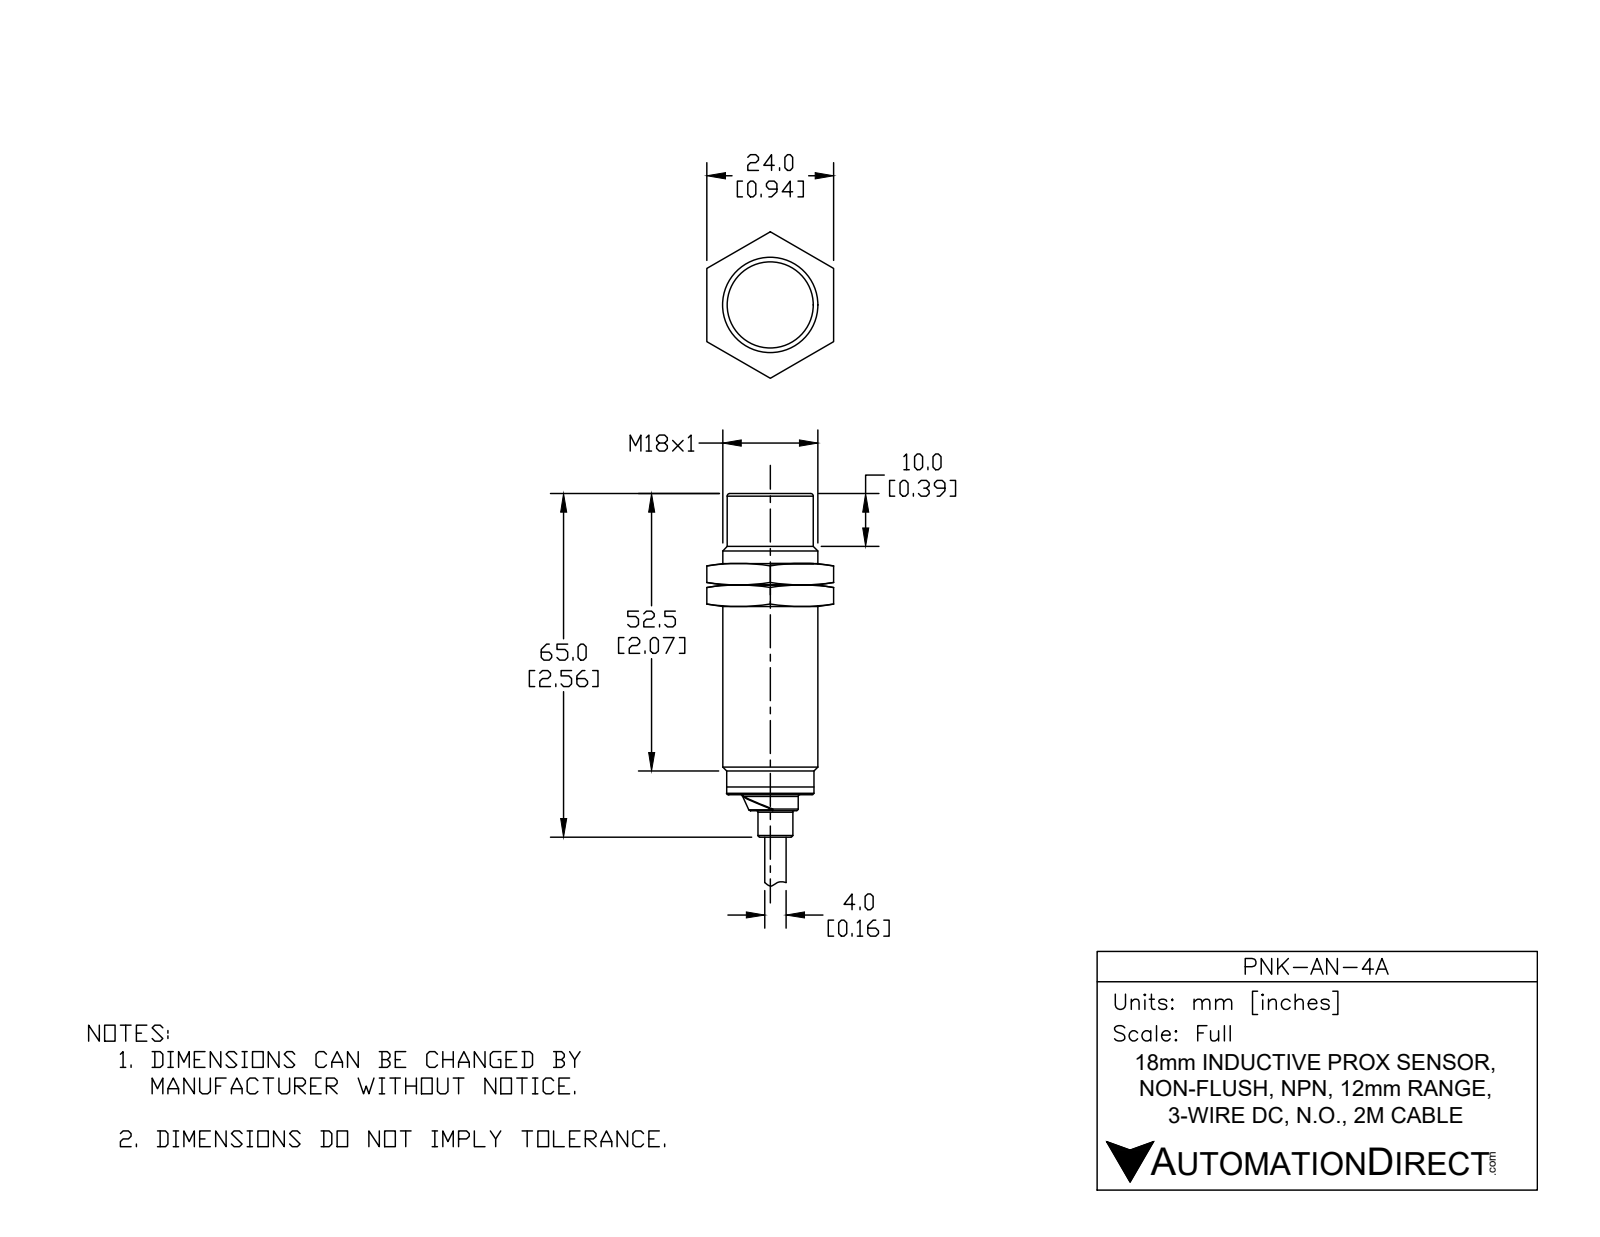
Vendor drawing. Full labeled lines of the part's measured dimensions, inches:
Part name (STEP PRODUCT): PNK-AN-4A
STEP written by: SolidWorks 2017 (AUTOMOTIVE_DESIGN)
Units: inches
Bodies: 1 solid, 76 faces (18 planar, 20 cylindrical, 38 other)
Overall size (bounding box): 4.559 × 0.709 × 0.709
Volume: 0.936 in³ · Surface area: 7.094 in²
Round holes (diameter × count): ⌀0.634 ×1
Round bosses / shafts (diameter × count): ⌀0.709 ×1, ⌀0.65 ×1, ⌀0.65 ×1, ⌀0.633 ×1, ⌀0.417 ×1, ⌀0.26 ×1, ⌀0.157 ×1
Partial cylindrical surfaces — rounded edges, fillets, slot ends (radius × count): R0.079 ×1, R0.081 ×1, R0.091 ×1
Main face-to-face distances: 2.244, 2.362, 0.118, 2.559, 0.315, 0.197, 4.559, 2.315, 2.197, 2
